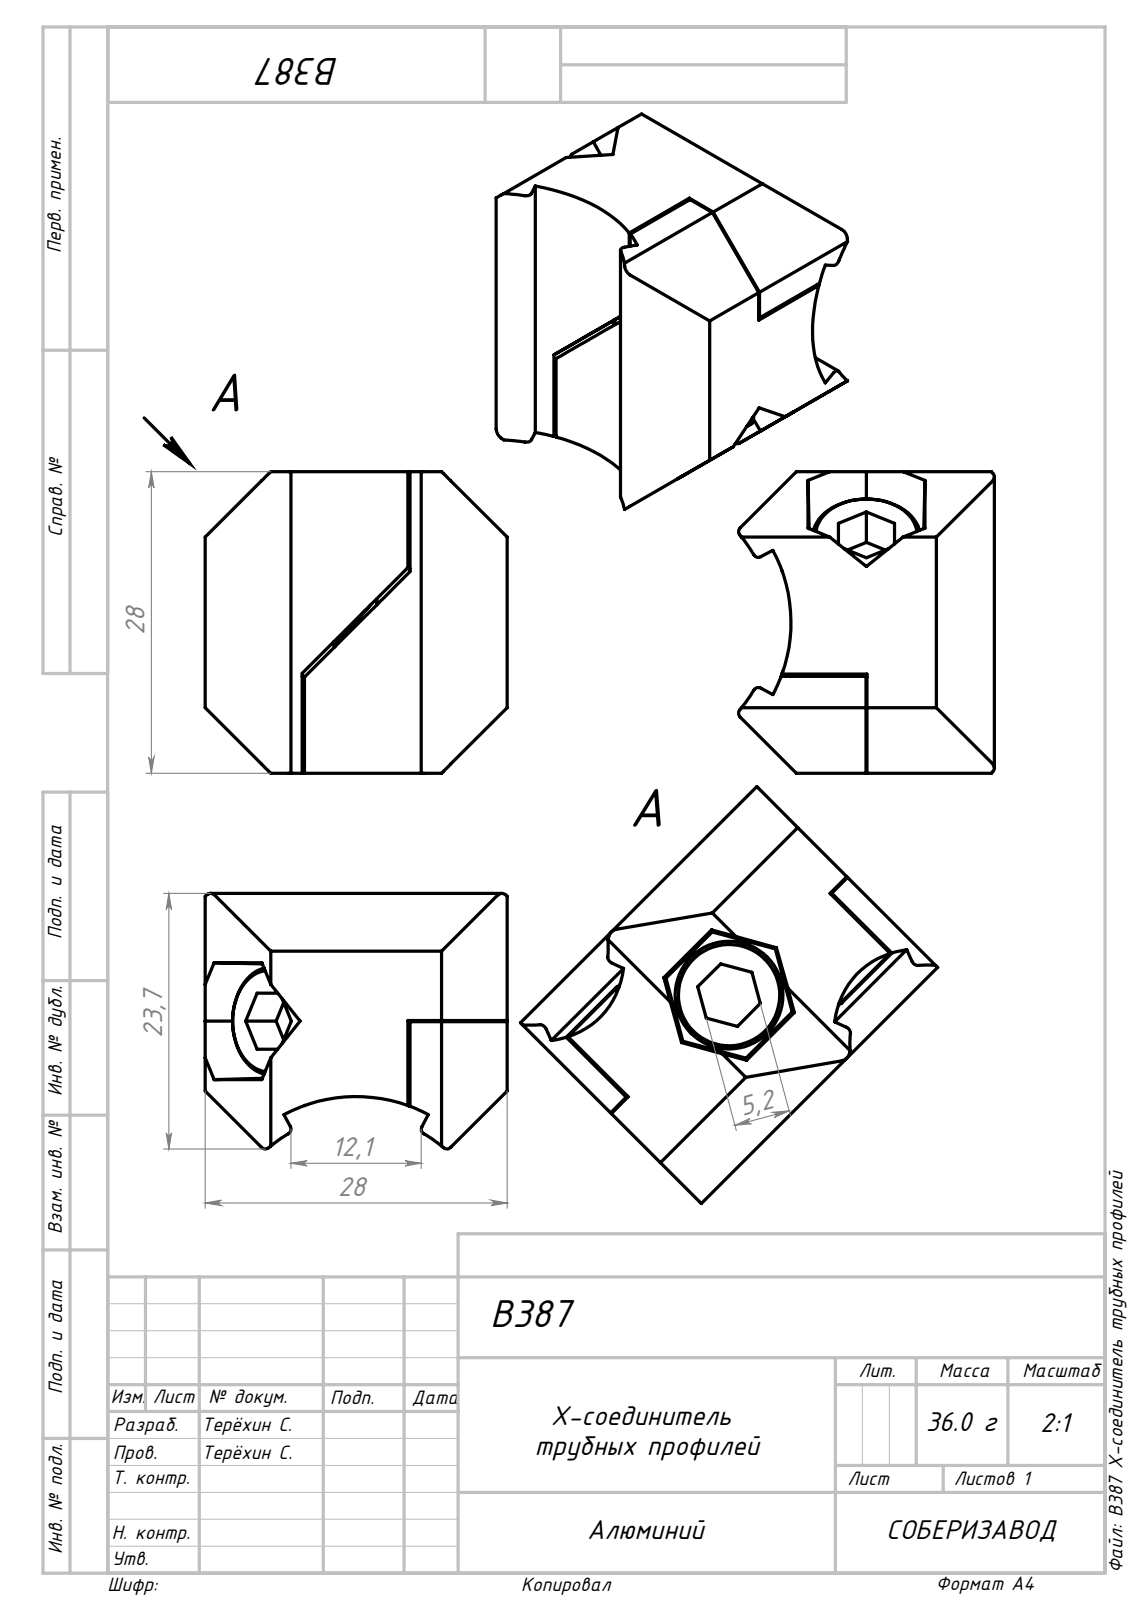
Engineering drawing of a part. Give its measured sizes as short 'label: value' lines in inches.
name: B387 Х-соединитель трубных профилей
written by: SolidWorks 2022 (AUTOMOTIVE_DESIGN)
unit: in
bodies: 4 solids, 187 faces (70 planar, 72 cylindrical, 45 other)
size: 1.102 × 1.102 × 0.934
volume: 0.69 in³; area: 10.64 in²
holes: 2× ⌀0.256, 1× ⌀0.205
bosses: 1× ⌀0.394, 1× ⌀0.236
rounds: 8× R0.02, 2× R0.49, 2× R0.559
face distances: 1.102, 0.394, 0.354, 0.748, 0.362, 0.74, 0.386, 0.406, 0.209, 0.224
